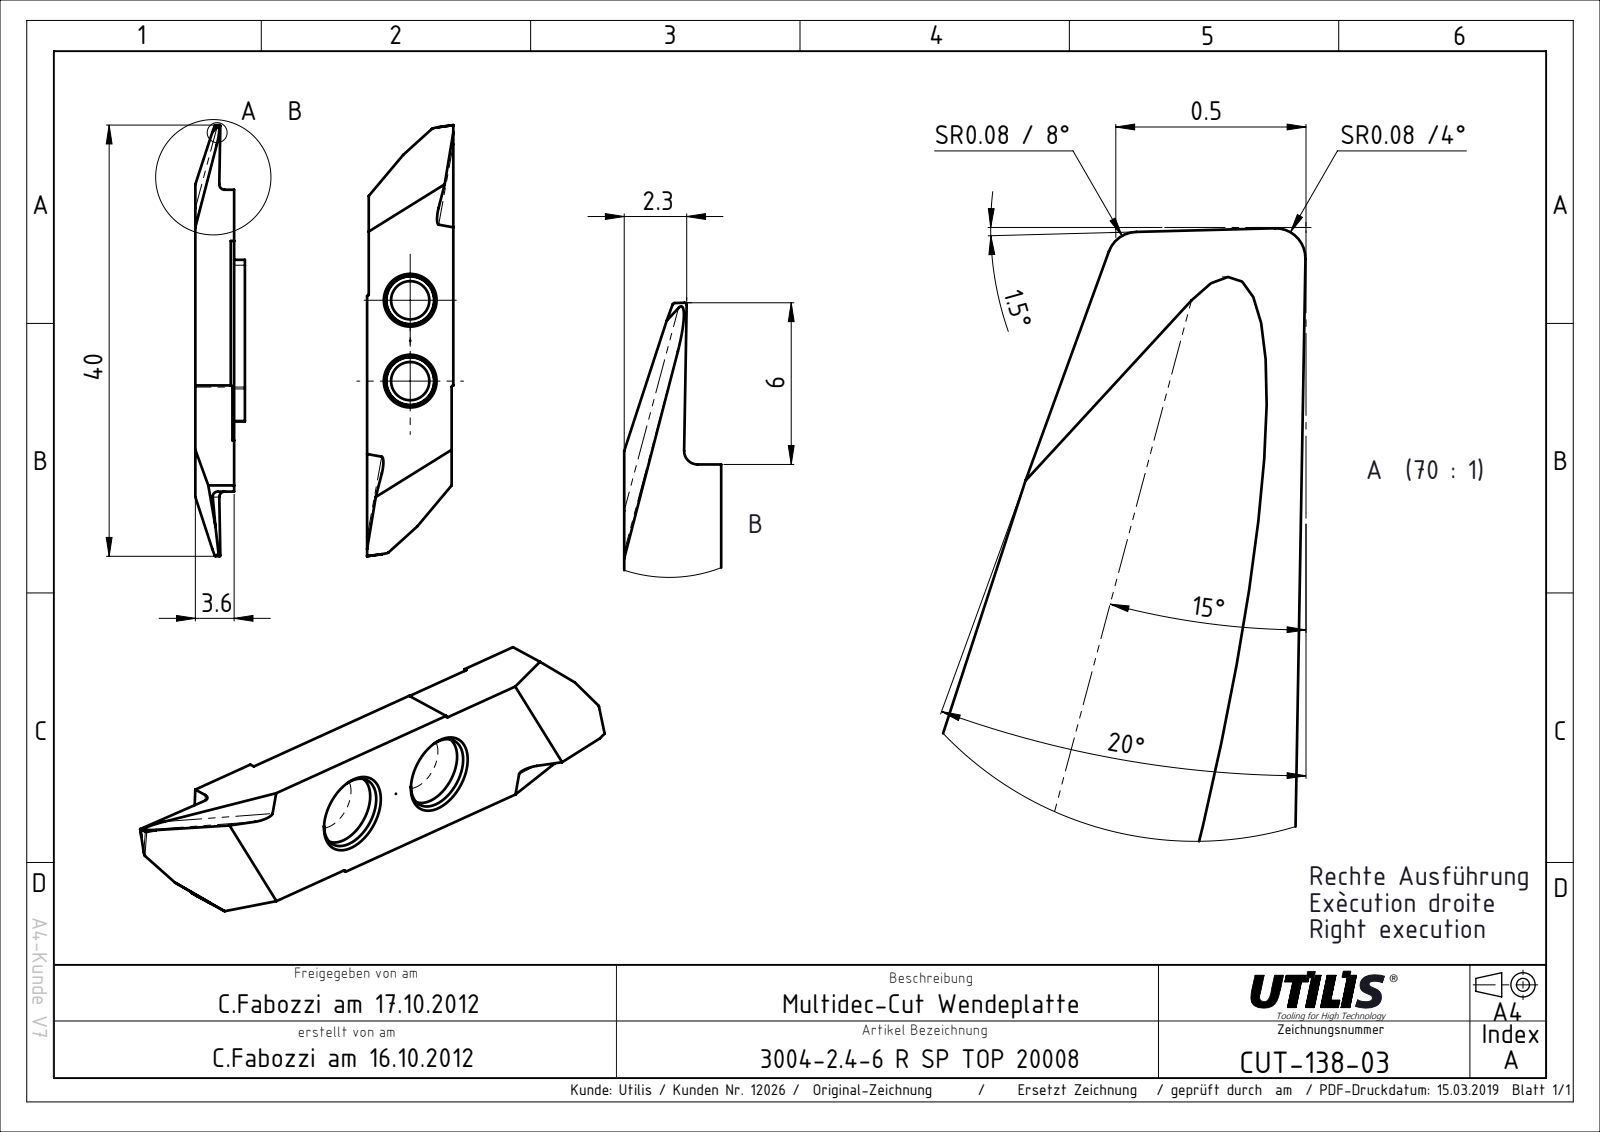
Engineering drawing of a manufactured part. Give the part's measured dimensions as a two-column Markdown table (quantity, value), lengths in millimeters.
| quantity | value |
| --- | --- |
| part name | CUT-138; ASME Y14.5 |
| STEP written by | FormatWorks Professional (AP242_MANAGED_MODEL_BASED_3D_ENGINEERING_MIM_LF) |
| units | millimeters |
| bodies | 1 solid, 40 faces (26 planar, 14 cylindrical, 0 other) |
| overall size | 40 × 8 × 3.6 |
| volume | 774 mm³ |
| surface area | 840 mm² |
| round holes (diameter × count) | 3.55 × 2 |
| partial cylindrical surfaces (radius × count) | 0.15 × 2, 0.5 × 2 |
| main face-to-face distances | 3.6, 8, 7.85, 7.7, 28, 23.16, 39.86, 4.75, 23.25, 18.5 |
| hole center spacings | 3.75, 7.5 |
